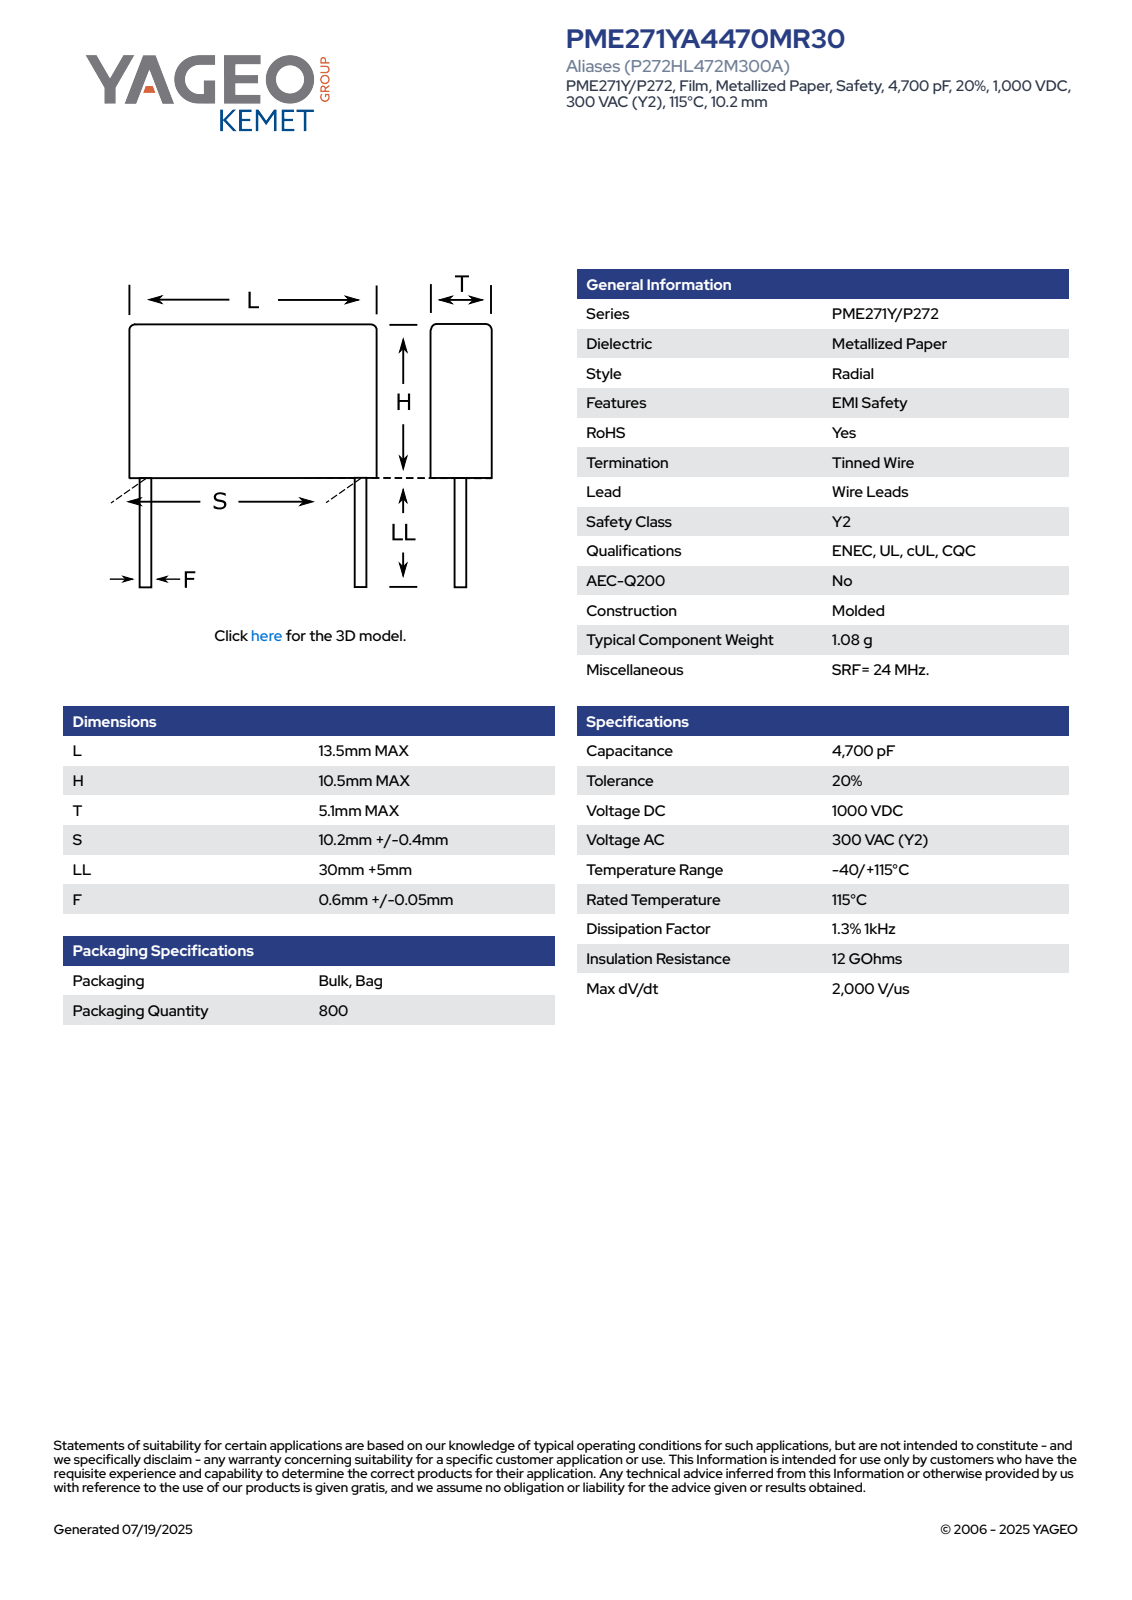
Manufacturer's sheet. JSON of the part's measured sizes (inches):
{"part_name": "CFR_MOLDED_13.5X10.5X5.1_L13.5H10.5T5.1S10.2LL35F0.65", "step_written_by": "SolidWorks 2014 (AUTOMOTIVE_DESIGN)", "units": "inches", "bodies": {"solids": 4, "faces": 73, "planar": 65, "cylindrical": 8, "other": 0}, "overall_size": [1.791, 0.531, 0.201], "volume_in3": 0.045, "surface_area_in2": 1.04, "round_bosses_or_shafts": [[0.026, 2]], "partial_cylinders_radius": [[0.02, 4]], "face_to_face_distances": [0.201, 0.413, 0.531, 1.378, 1.791, 0.048, 1.599, 0.221, 0.193, 1.551]}
